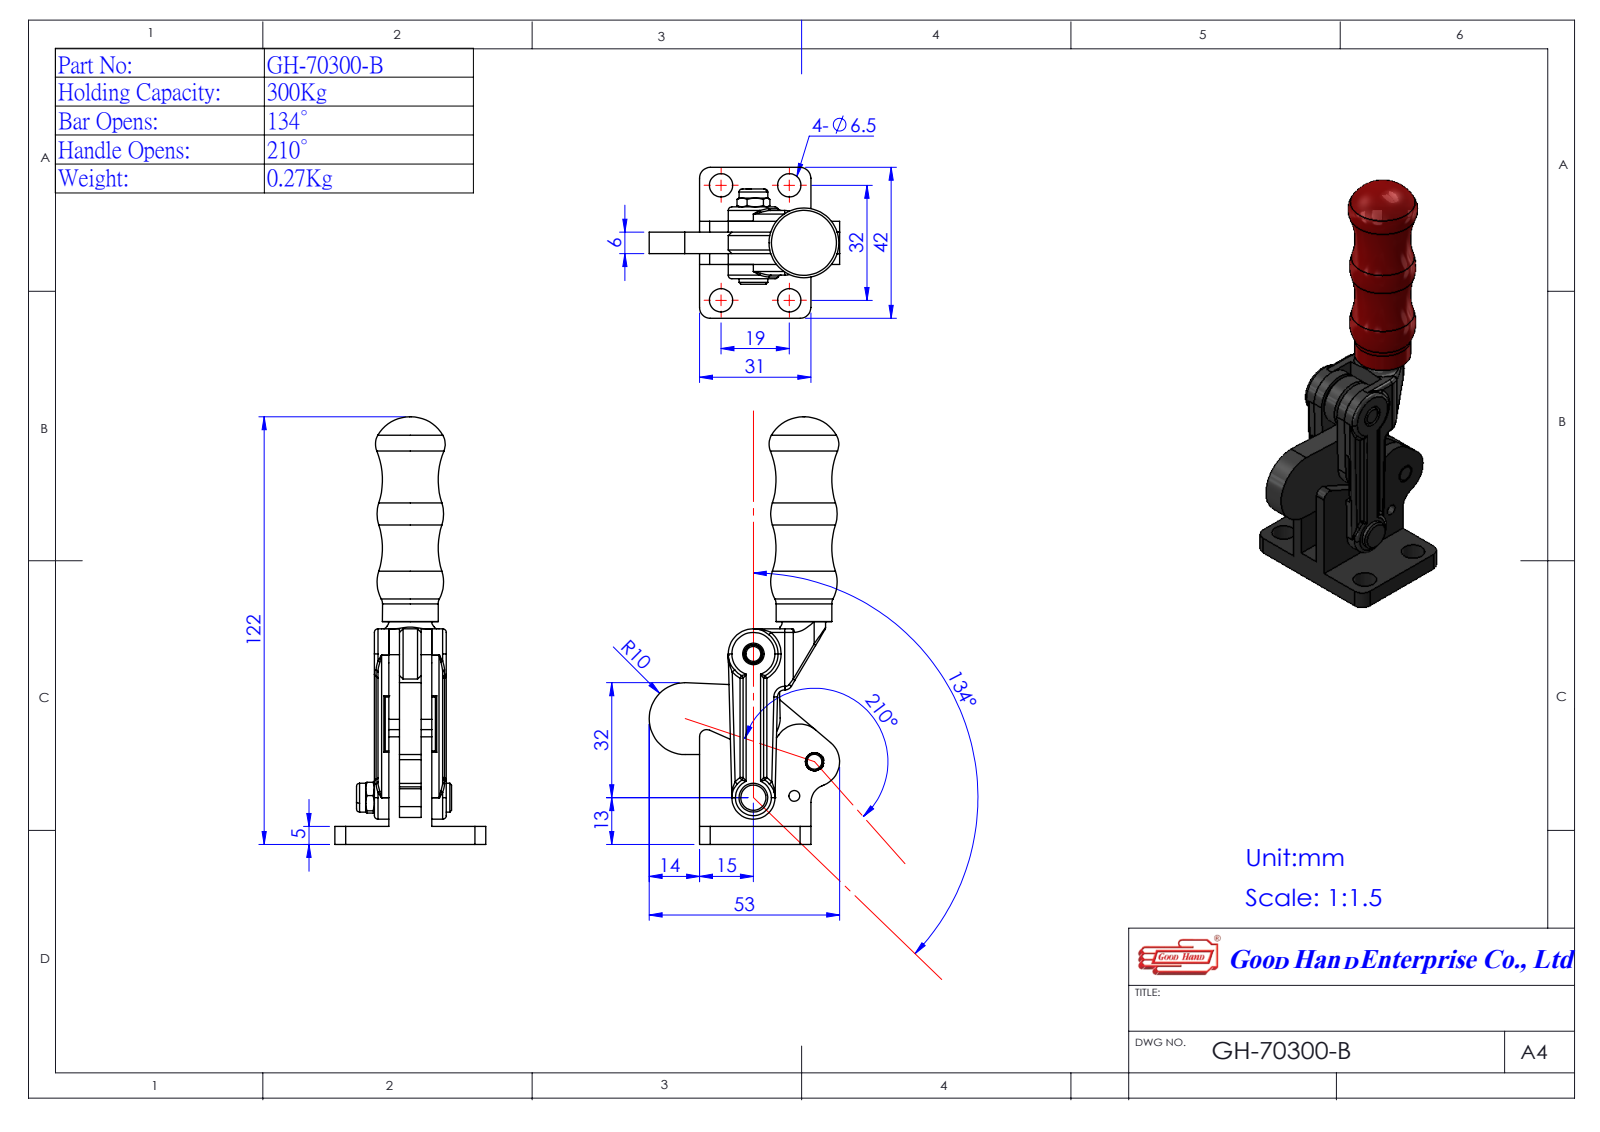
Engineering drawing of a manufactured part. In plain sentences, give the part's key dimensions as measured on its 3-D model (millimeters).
The part is named "Group2^GH-70300-B(簡化); Group1_GH-70320(簡化); Group1^Group1_GH-70320(簡化); GH-70300-B(簡化) (+2 more)". Its 3-D file was written by "SolidWorks 2016 (AUTOMOTIVE_DESIGN)". It is 4 solids with 229 faces: 58 planar, 88 cylindrical and 83 other. Overall it measures 119.02 by 53 by 42 millimeters. Its volume is 40 848 cubic millimeters and its surface area 20 255 square millimeters. Round holes: 4 of diameter 4, 4 of diameter 6.5, 1 of diameter 3. Round bosses or shafts: 1 of diameter 14. Partial cylindrical surfaces (rounded edges, fillets, slot ends): 19 of radius 1, 4 of radius 3, 3 of radius 2, 3 of radius 5, 3 of radius 7, 3 of radius 10, 2 of radius 6, 1 of radius 8. The main face-to-face distances are 3, 9, 6, 12, 4, 13, 7, 16, 5, 20. The hole center spacings are 19, 32, 37.22, 11.03, 11.41, 18, 19.72, 20.43.
